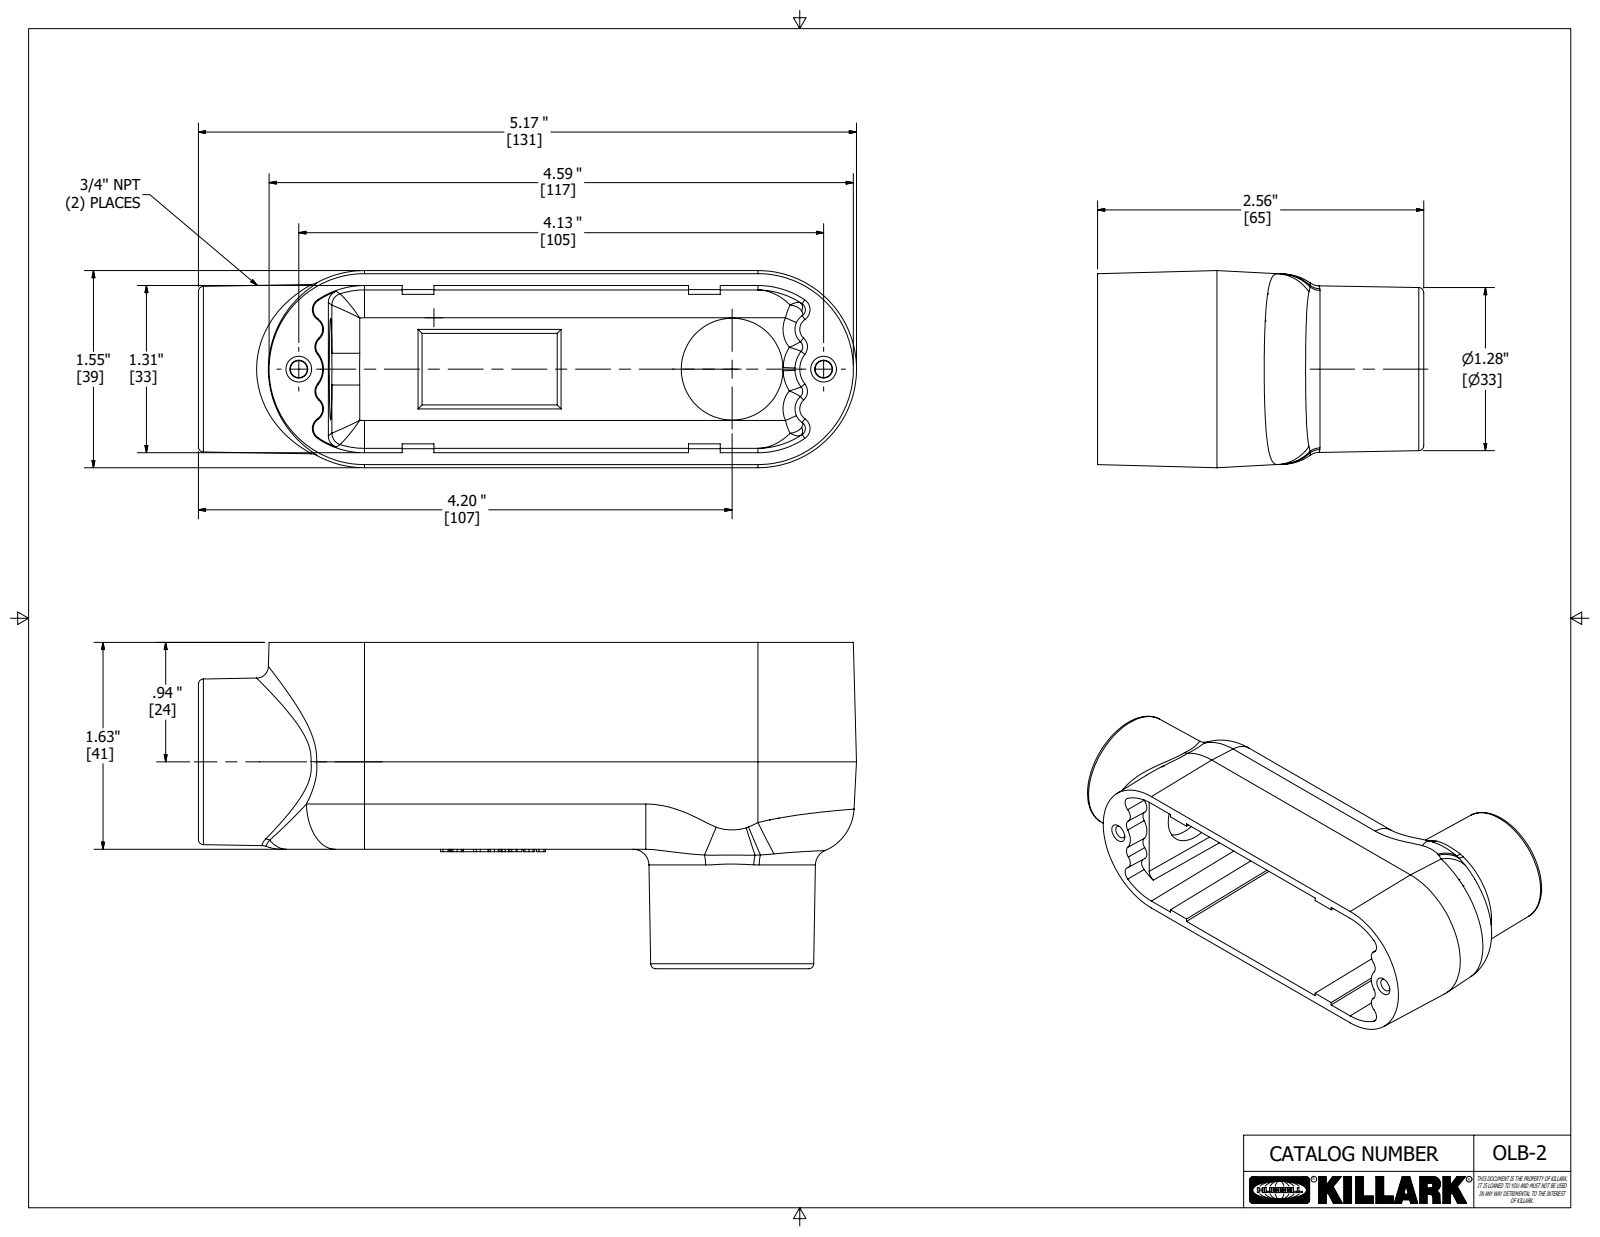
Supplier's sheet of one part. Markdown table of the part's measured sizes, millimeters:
| quantity | value |
| --- | --- |
| part name | 13770-1 |
| STEP written by | Autodesk Inventor 2018 (AUTOMOTIVE_DESIGN) |
| units | millimeters |
| bodies | 1 solid, 374 faces (171 planar, 12 cylindrical, 191 other) |
| overall size | 131.4 × 65.1 × 39.3 |
| volume | 64 200 mm³ |
| surface area | 35 000 mm² |
| round holes (diameter × count) | 20.3 × 2 |
| partial cylindrical surfaces (radius × count) | 0.8 × 4, 5.6 × 3, 9.5 × 2 |
| main face-to-face distances | 35.7, 2.4, 0.8, 34.9, 38.9, 41.3, 0.8, 3.1, 38.1, 1.6 |
